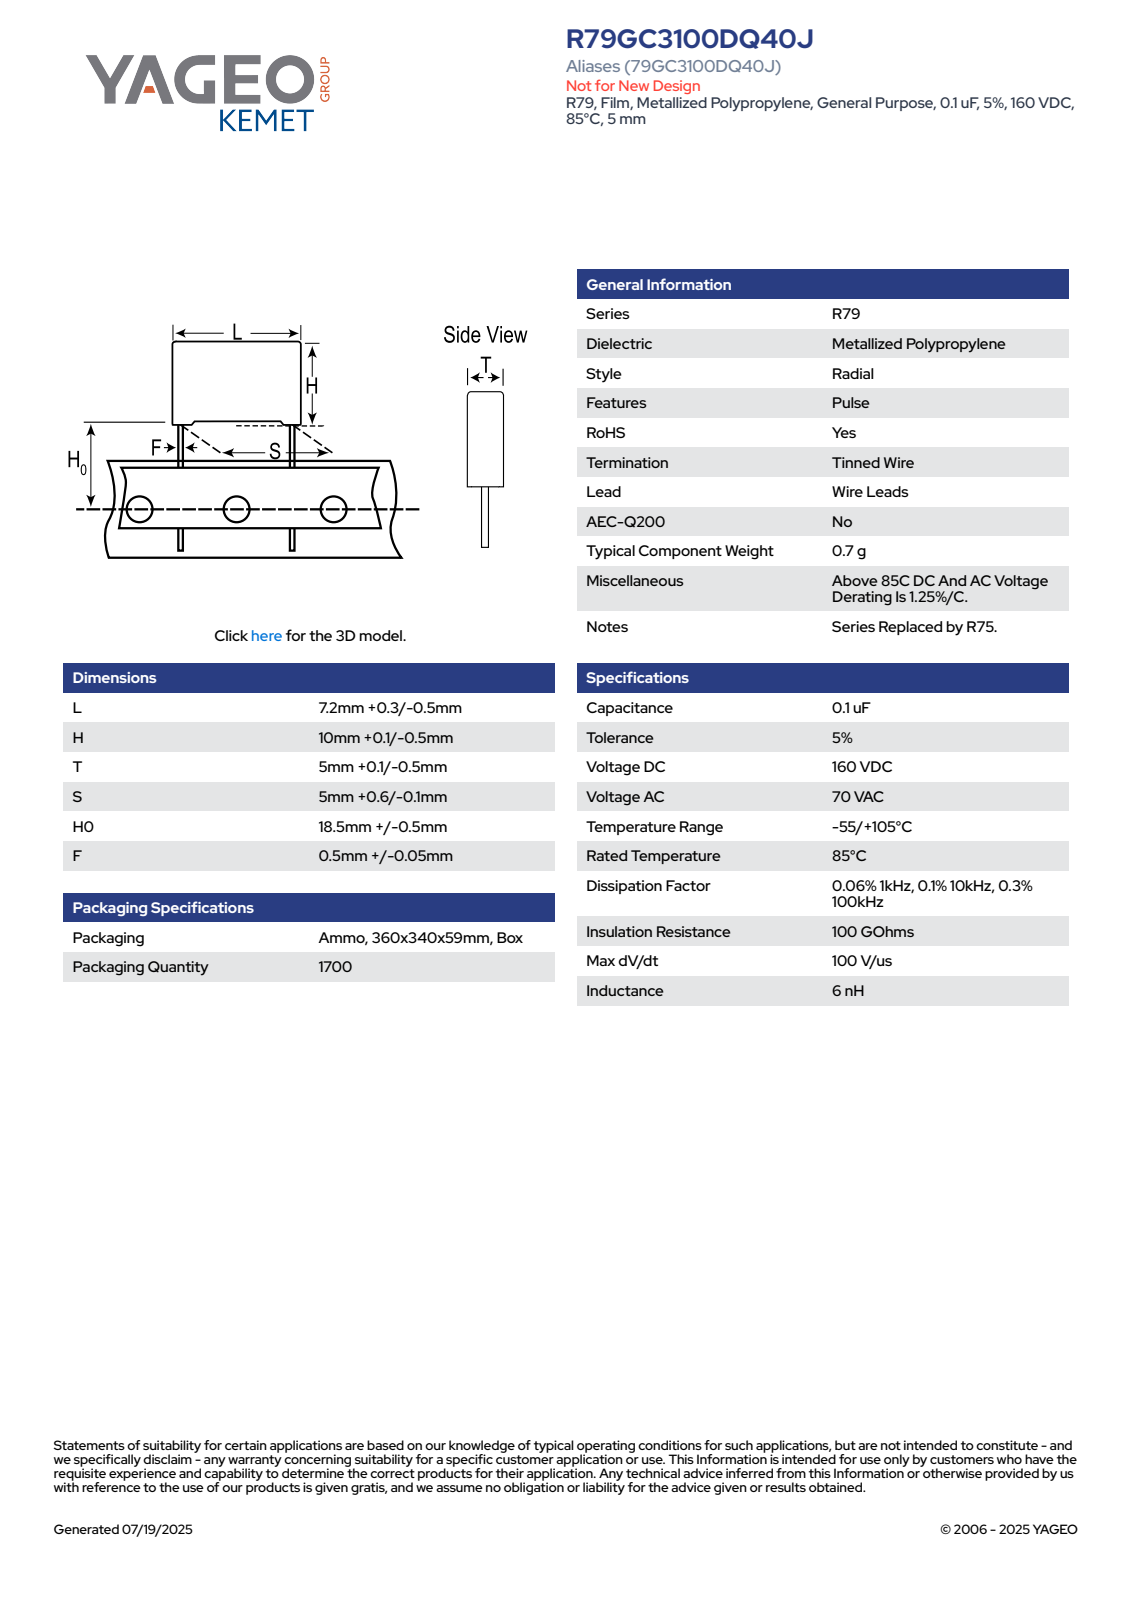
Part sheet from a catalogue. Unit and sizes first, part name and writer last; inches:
Units: inches
Overall size (bounding box): 1.146 × 0.295 × 0.201
Round bosses / shafts (diameter × count): ⌀0.022 ×2
Partial cylindrical surfaces — rounded edges, fillets, slot ends (radius × count): R0.02 ×4
Main face-to-face distances: 0.201, 0.295, 0.368, 0.191, 0.285, 0.03, 0.398, 0.181, 0.276, 0.014
Volume: 0.023 in³ · Surface area: 0.64 in²
Bodies: 4 solids, 85 faces (77 planar, 8 cylindrical, 0 other)
Part name (STEP PRODUCT): CFR_RB2_7.2X10X5_L7.5H10.1T5.1S5H019F0.55
STEP written by: SolidWorks 2020 (AUTOMOTIVE_DESIGN)
